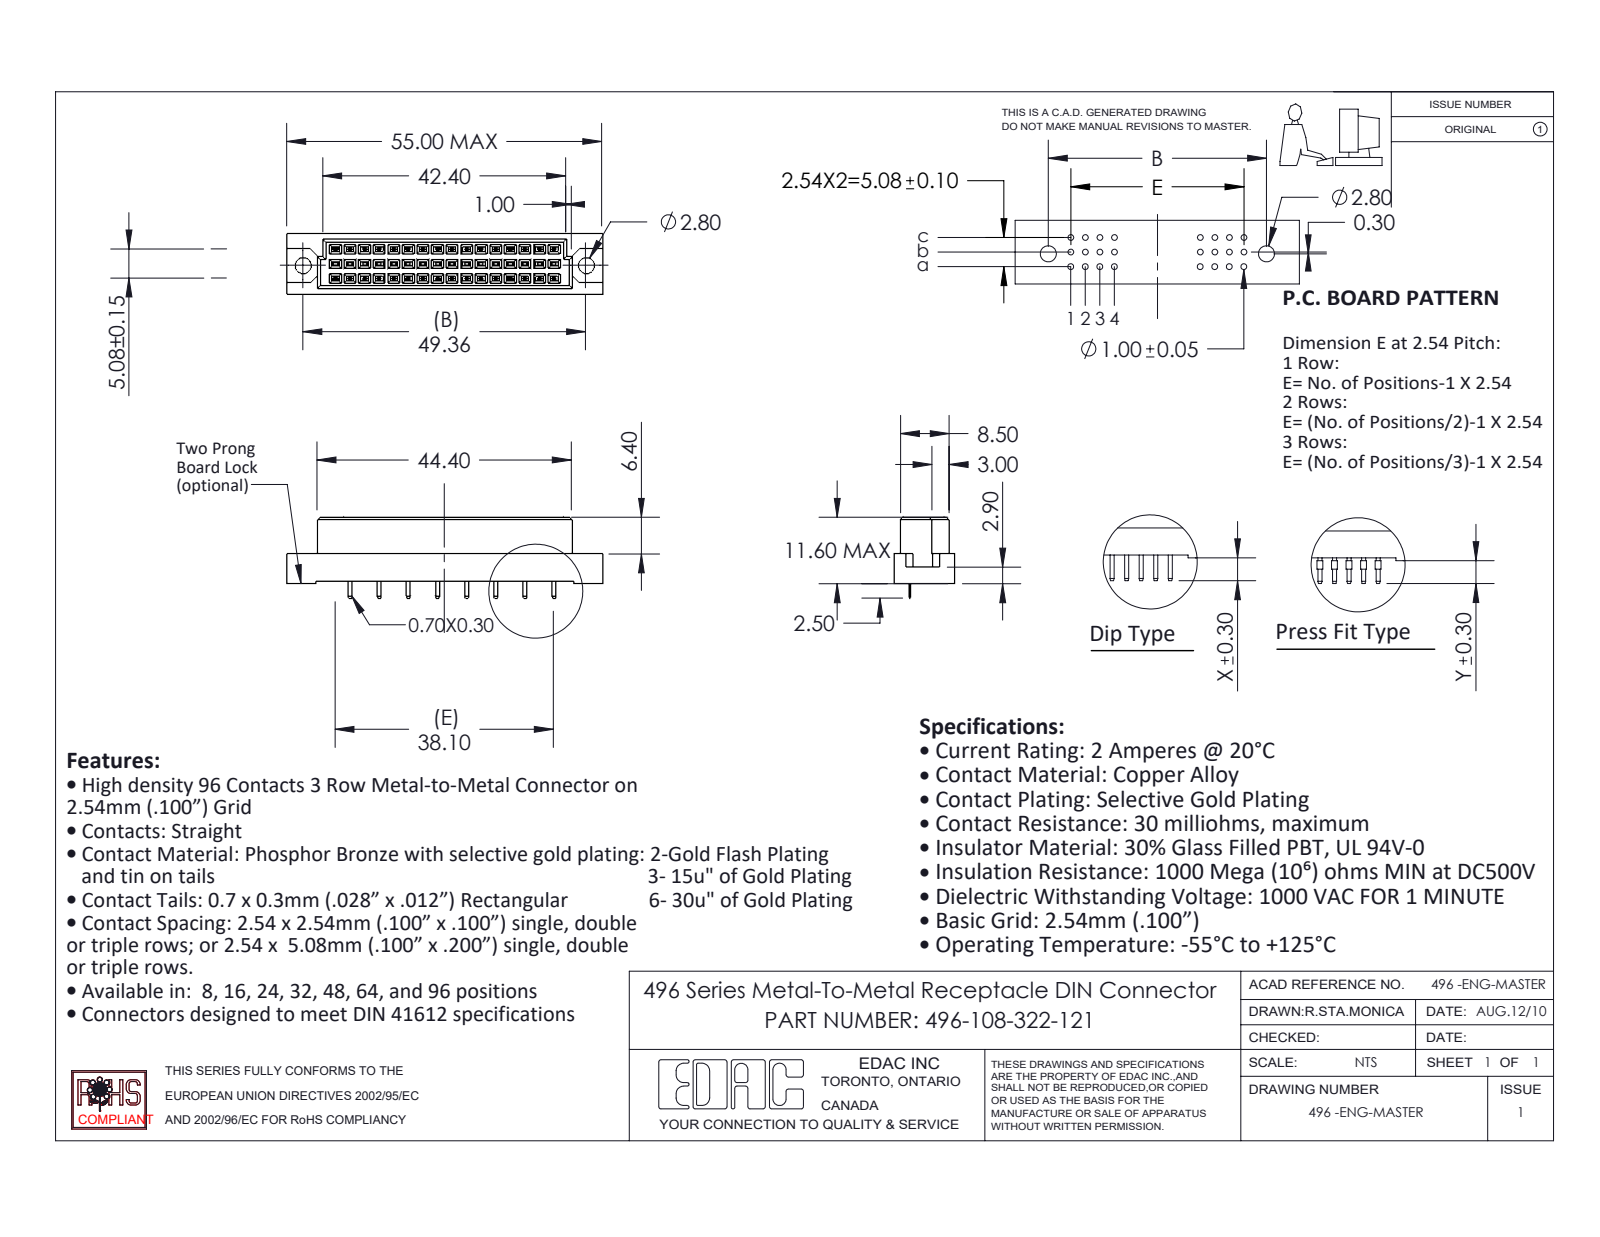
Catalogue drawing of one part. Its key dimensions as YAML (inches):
part_name: "496-108-322-121; 496-290_22; 496 Part_48"
step_written_by: "SolidWorks 2020 (CONFIG_CONTROL_DESIGN)"
units: inches
bodies: {solids: 9, faces: 746, planar: 742, cylindrical: 4, other: 0}
overall_size: [2.165, 0.555, 0.417]
volume: 0.281
surface_area: 6.716
round_holes:
  - {diameter: 0.11, count: 2}
face_to_face_distances: [0.1, 0.2, 0.041, 0.376, 0.032, 0.417, 0.132, 0.068, 0.335, 0.022]
hole_center_spacings: [1.943]
